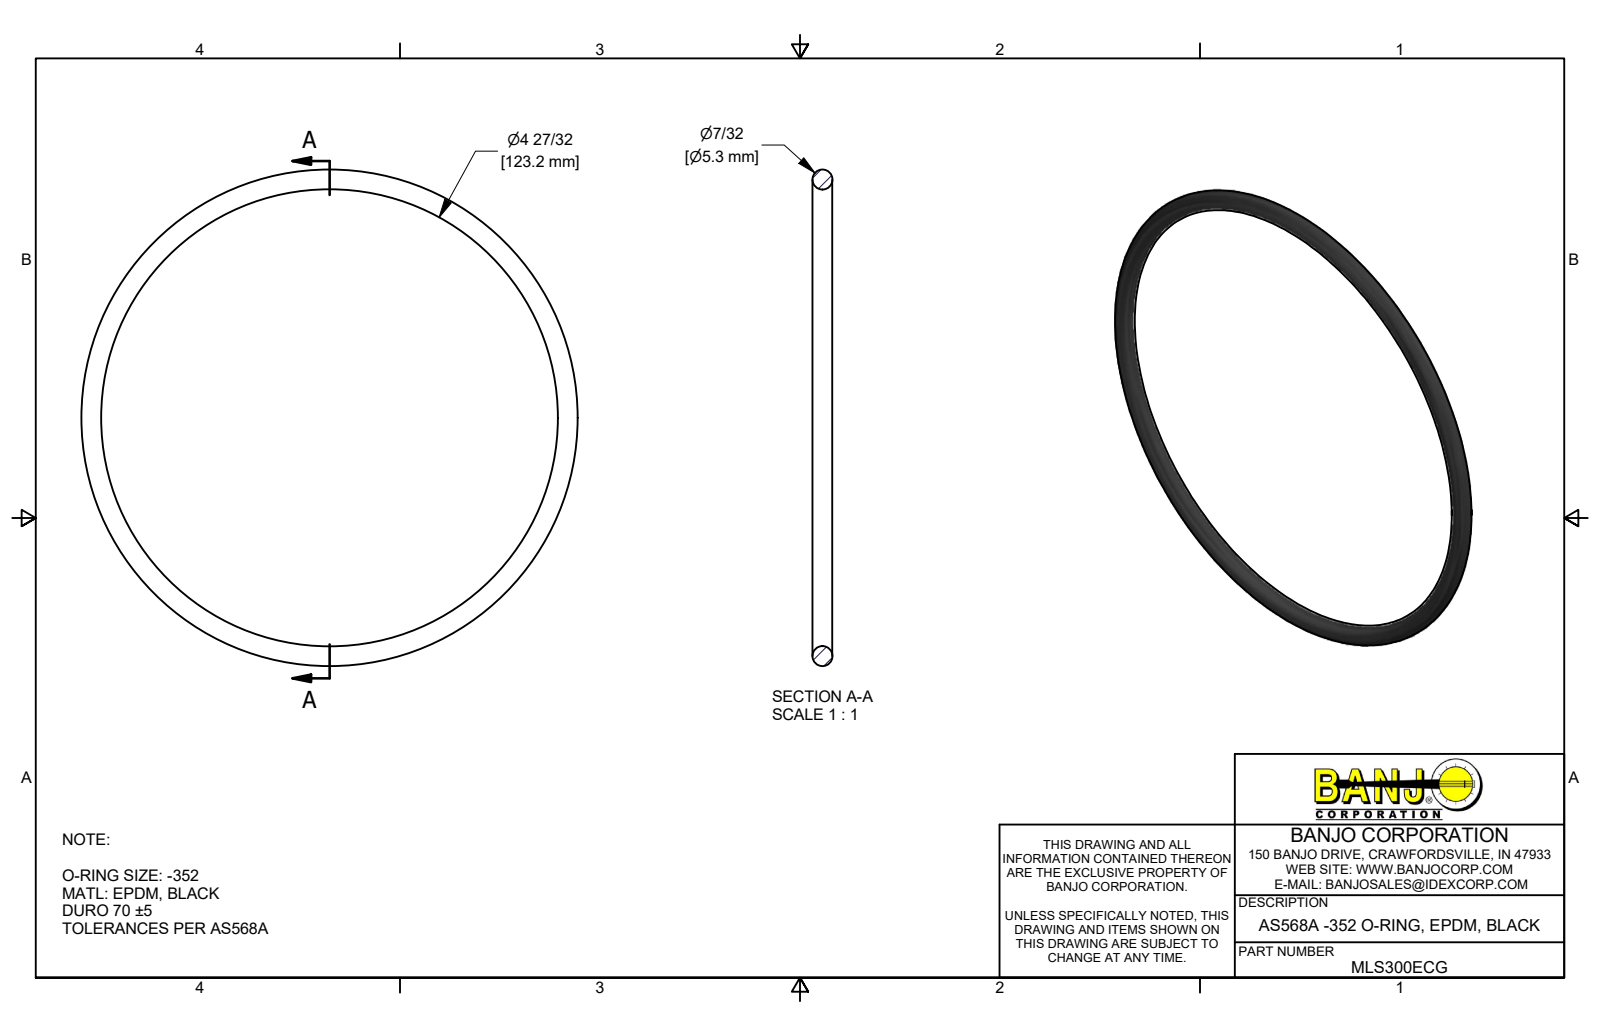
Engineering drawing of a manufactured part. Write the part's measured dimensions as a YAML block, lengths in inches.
part_name: "MLS300ECG"
step_written_by: "Autodesk Inventor 2019 (AUTOMOTIVE_DESIGN)"
units: inches
bodies: {solids: 1, faces: 1, planar: 0, cylindrical: 0, other: 1}
overall_size: [5.27, 5.27, 0.21]
volume: 0.551
surface_area: 10.49
